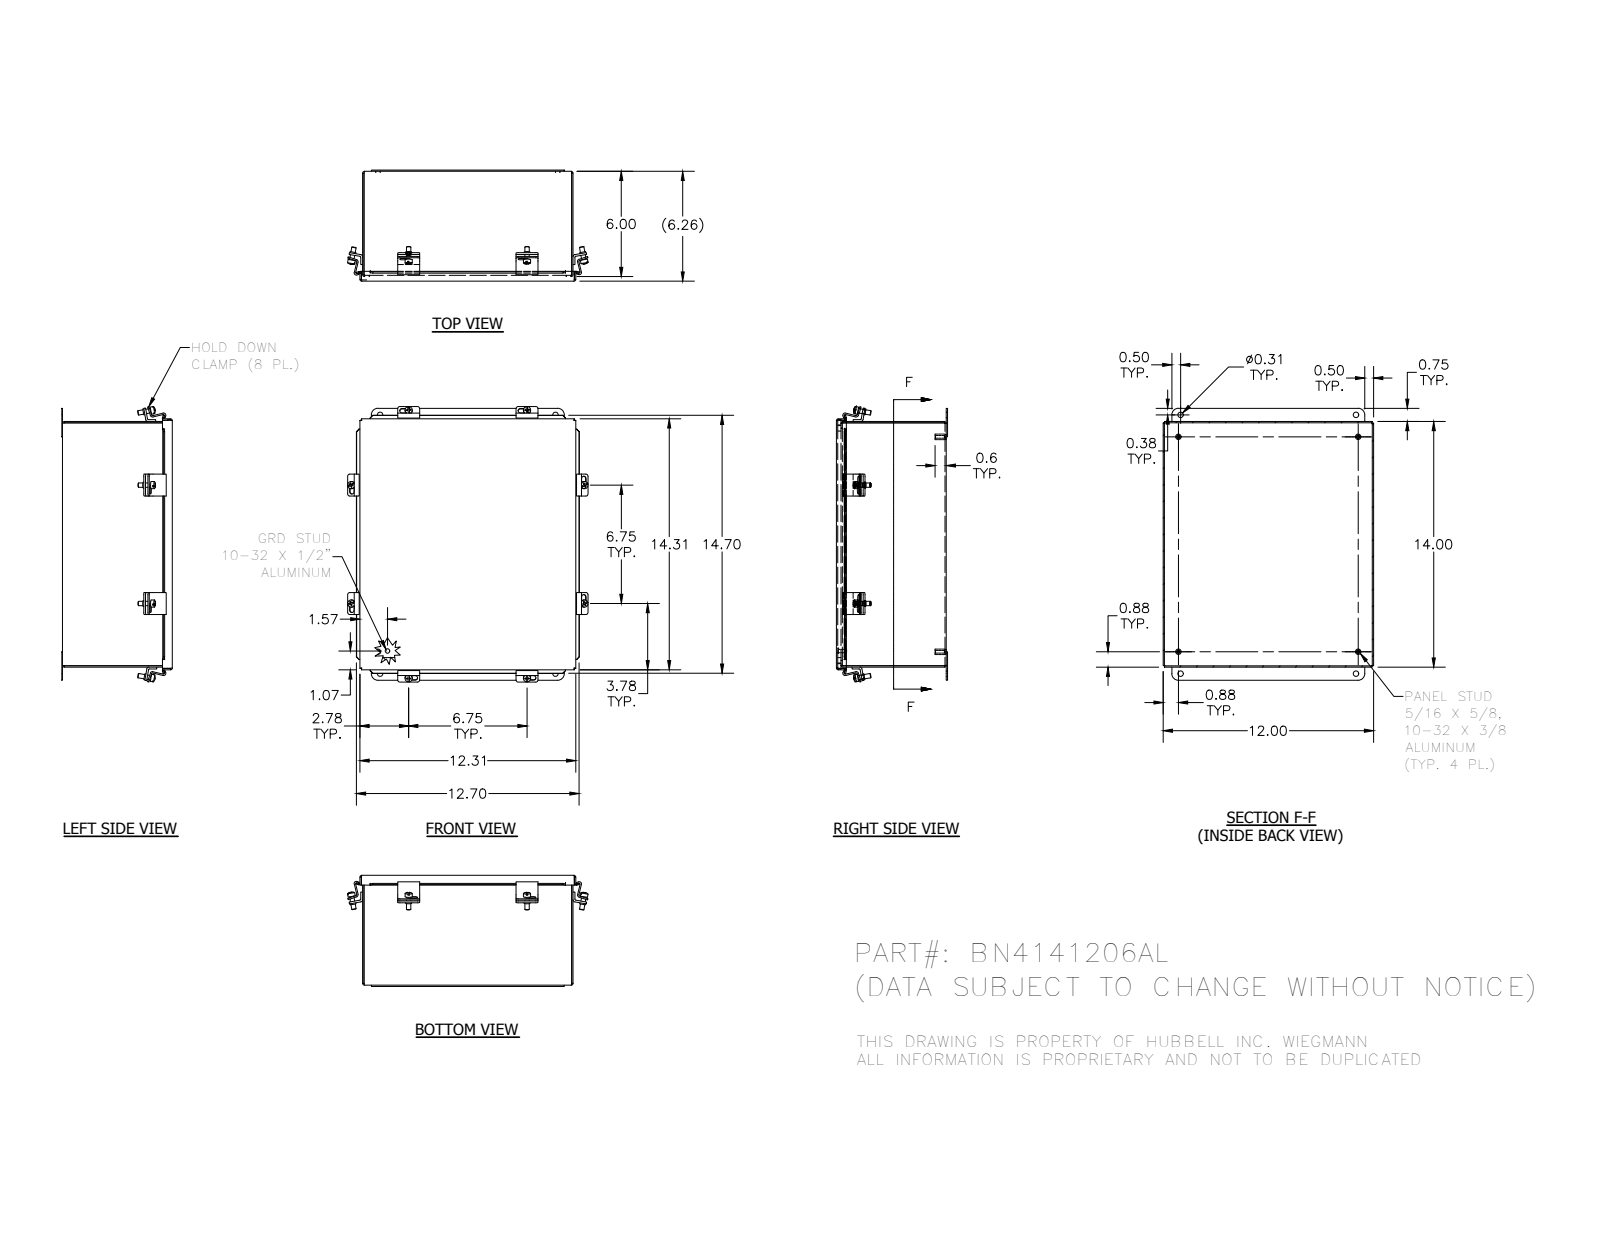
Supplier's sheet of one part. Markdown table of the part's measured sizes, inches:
| quantity | value |
| --- | --- |
| part name | 372135_1; 316168_1; BN41412ALLID_1; 3086_1 (+6 more) |
| STEP written by | SolidWorks 2014 (AUTOMOTIVE_DESIGN) |
| units | inches |
| bodies | 35 solids, 781 faces (431 planar, 272 cylindrical, 78 other) |
| overall size | 15.706 × 13.711 × 6.336 |
| volume | 62.78 in³ |
| surface area | 1 630 in² |
| round holes (diameter × count) | 0.196 × 8, 0.156 × 4, 0.25 × 4, 0.31 × 4 |
| round bosses / shafts (diameter × count) | 0.25 × 11, 0.41 × 8, 0.344 × 8, 0.313 × 4, 0.19 × 1 |
| partial cylindrical surfaces (radius × count) | 0.125 × 32, 0.031 × 16, 0.105 × 16, 0.133 × 16, 0.063 × 12, 0.126 × 12, 0.375 × 4 |
| main face-to-face distances | 0.074, 6.187, 6.261, 6.113, 11.926, 13.926, 12, 11.852, 14, 13.852 |
| hole center spacings | 10.25, 1.256, 6.75, 13.5, 10.202, 10.202, 16.875, 1.256 |
